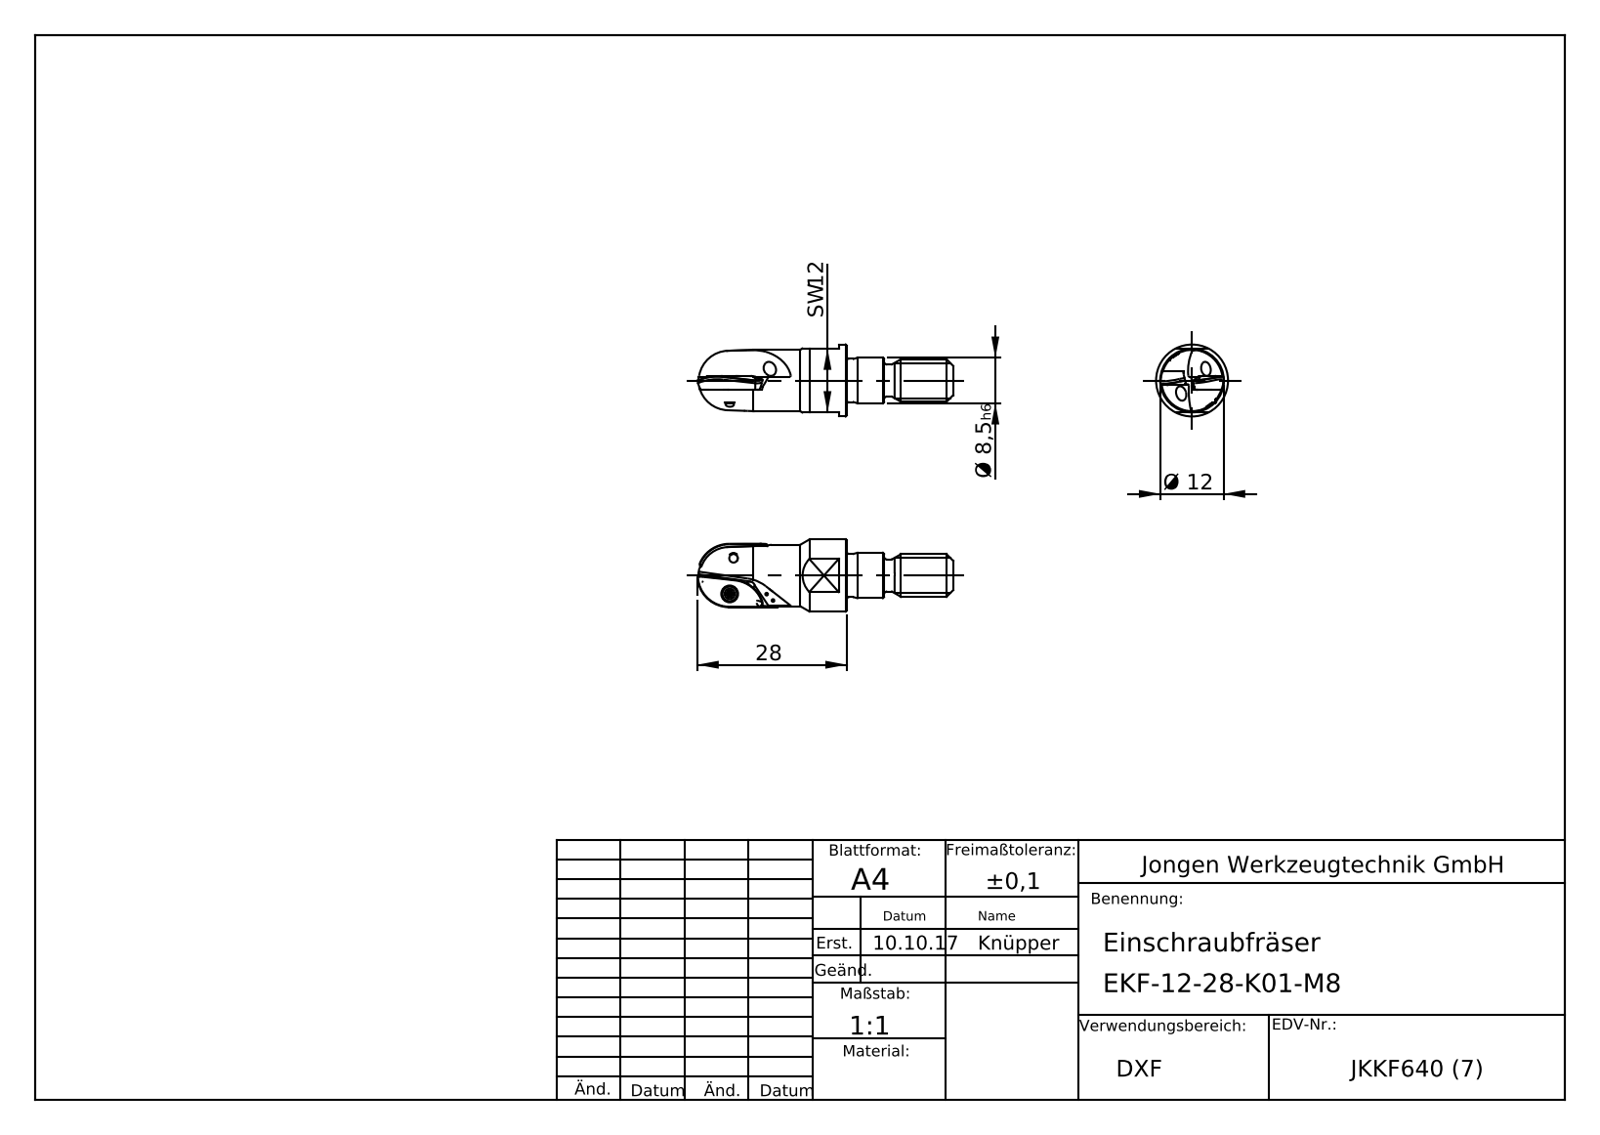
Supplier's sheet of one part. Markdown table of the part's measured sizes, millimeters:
| quantity | value |
| --- | --- |
| part name | EKF-12-28-K01-M8 |
| STEP written by | SolidWorks 2019 (AUTOMOTIVE_DESIGN) |
| units | millimeters |
| bodies | 1 solid, 111 faces (29 planar, 25 cylindrical, 57 other) |
| overall size | 48 × 13.5 × 13.5 |
| volume | 3 737 mm³ |
| surface area | 2 162 mm² |
| round holes (diameter × count) | 2.5 × 3 |
| round bosses / shafts (diameter × count) | 13.5 × 1, 11.5 × 1, 8.5 × 1, 8.1 × 1, 8 × 1, 6 × 1 |
| partial cylindrical surfaces (radius × count) | 0.2 × 4, 5 × 1, 7 × 1 |
| main face-to-face distances | 12, 20, 5.26, 6.74, 6.73, 1.47, 5.27, 7, 13, 1.5 |
